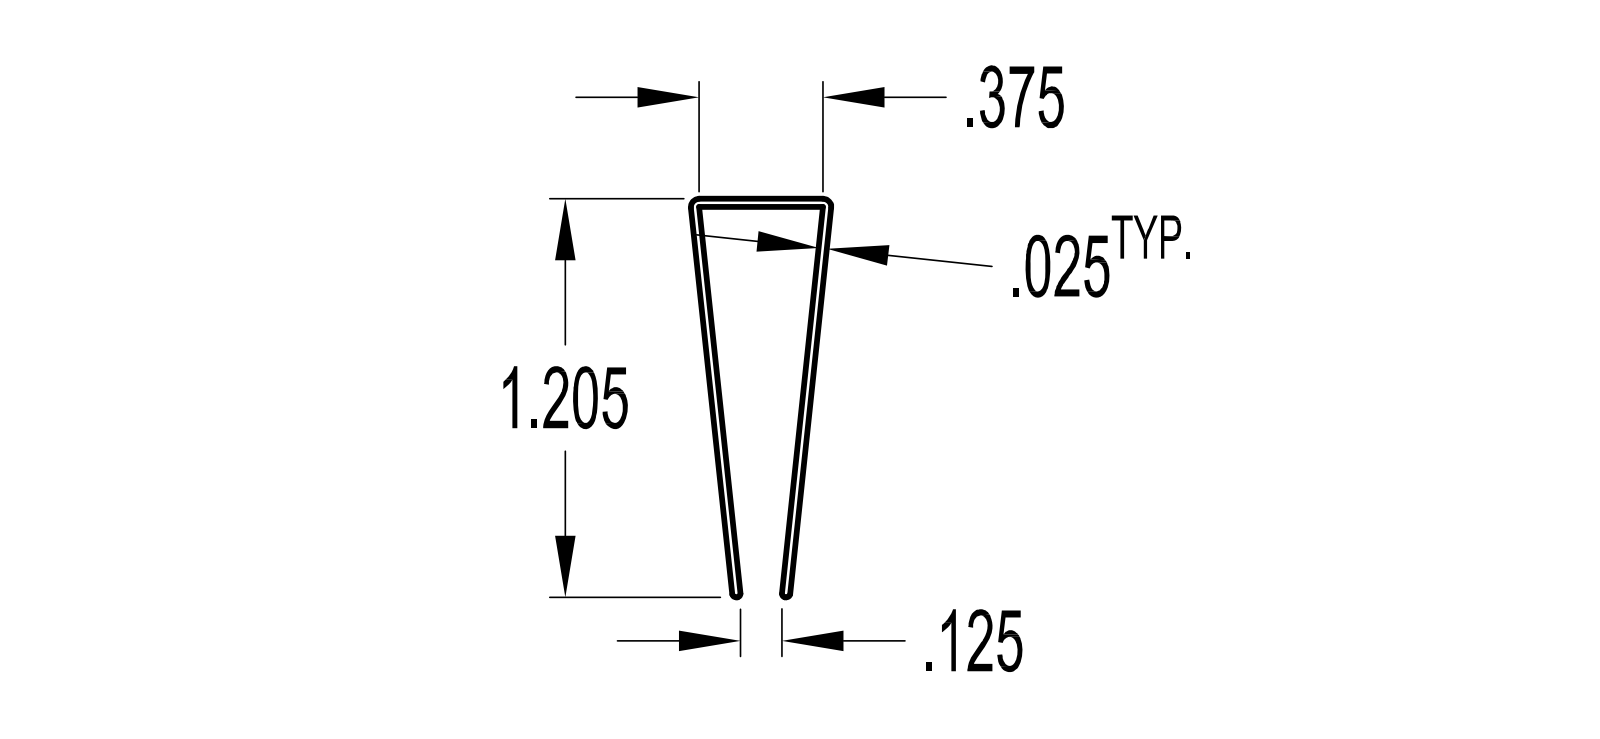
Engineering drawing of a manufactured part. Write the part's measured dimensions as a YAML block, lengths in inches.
step_written_by: "KeyCreator Pro (AUTOMOTIVE_DESIGN)"
units: inches
bodies: {solids: 1, faces: 16, planar: 10, cylindrical: 6, other: 0}
overall_size: [6, 1.205, 0.425]
volume: 0.418
surface_area: 33.79
partial_cylinders:
  - {radius: 0.01, count: 4}
  - {radius: 0.025, count: 2}
face_to_face_distances: [0.025, 0.025, 6]
